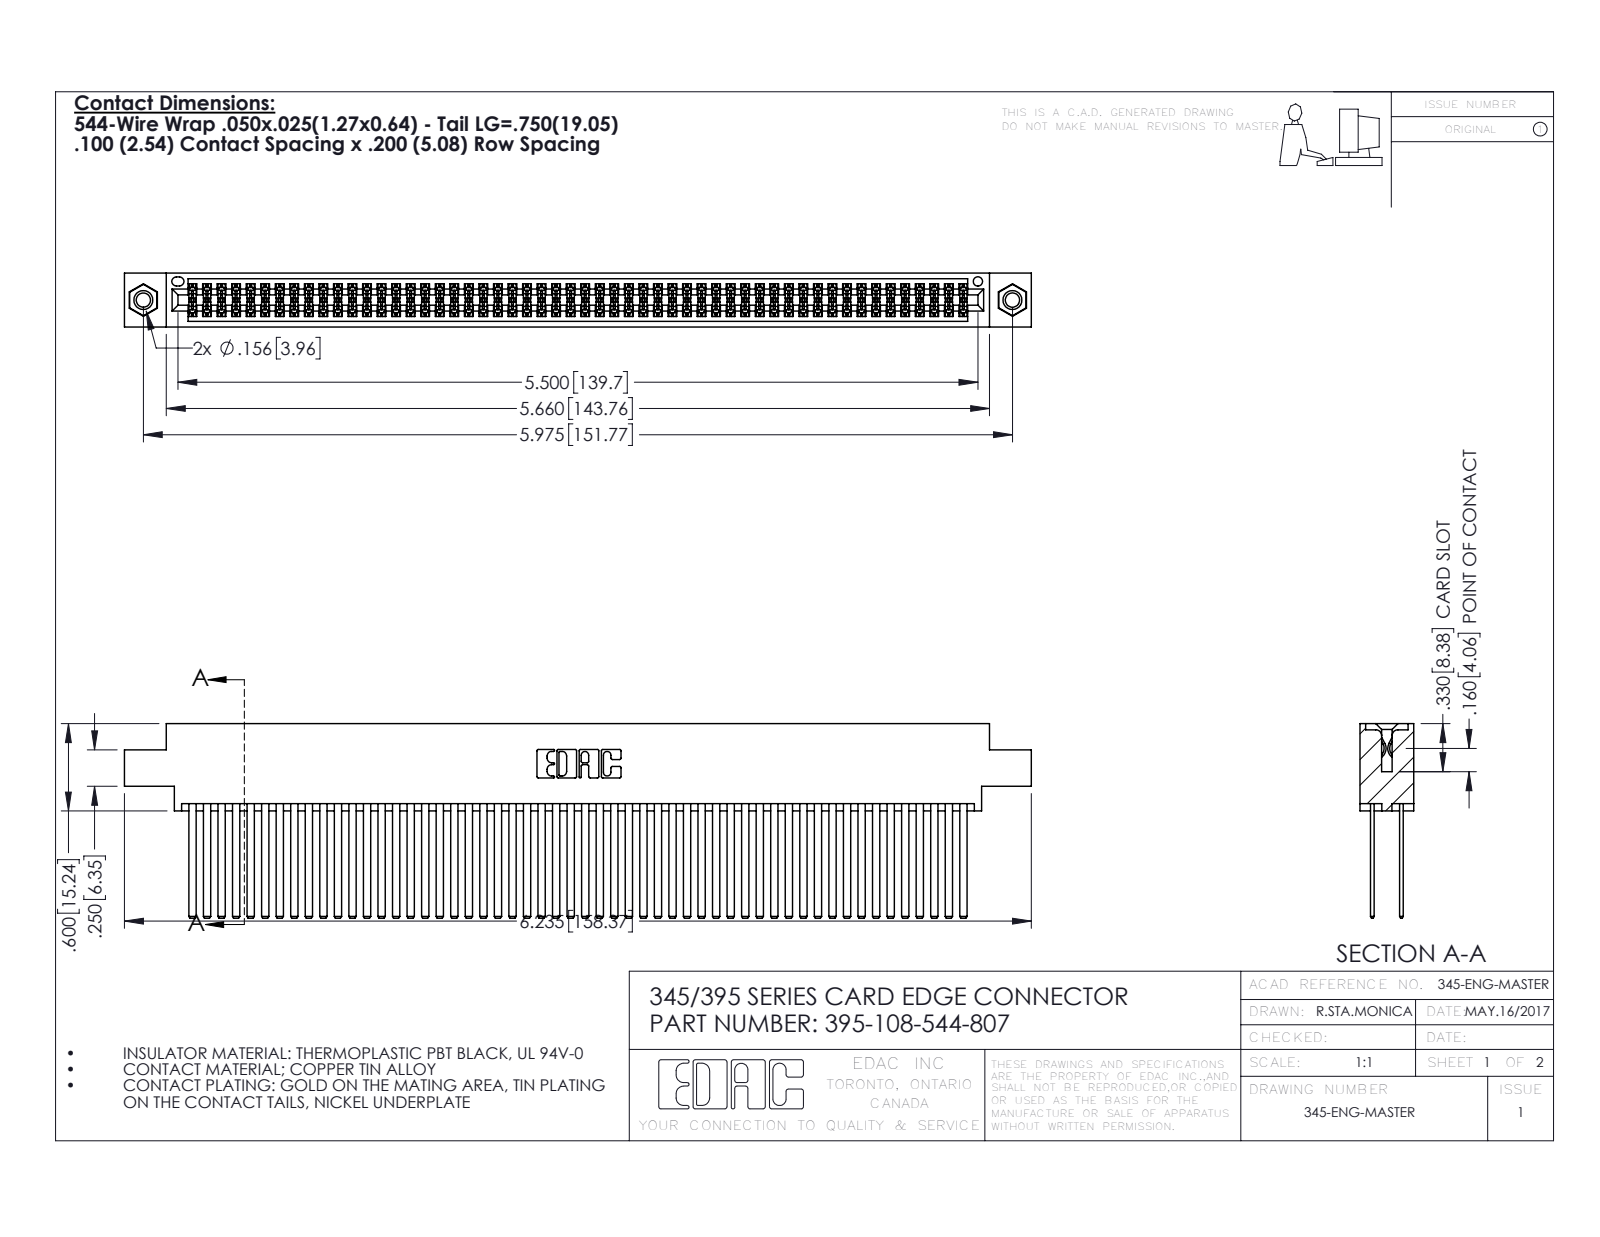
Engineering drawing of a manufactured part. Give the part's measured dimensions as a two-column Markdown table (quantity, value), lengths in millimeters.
| quantity | value |
| --- | --- |
| part name | 395-108-544-807; 345 Part_0.170 Offset - 0.156 Dia-TI; 345-250-001_345-250-005-103; 345-292-001_345-293-144 |
| STEP written by | SolidWorks 2016 (CONFIG_CONTROL_DESIGN) |
| units | millimeters |
| bodies | 111 solids, 4942 faces (3248 planar, 1678 cylindrical, 16 other) |
| overall size | 158.4 × 34 × 9.4 |
| volume | 16 880 mm³ |
| surface area | 29 790 mm² |
| round holes (diameter × count) | 2.5 × 2, 3.2 × 2, 4 × 2, 1.6 × 1 |
| round bosses / shafts (diameter × count) | 3.9 × 2 |
| partial cylindrical surfaces (radius × count) | 0.2 × 162, 0.3 × 22, 0.2 × 6, 0.8 × 6, 0.7 × 3, 0.4 × 2, 0.5 × 2, 0.6 × 2 |
| main face-to-face distances | 5.1, 0.6, 1.8, 2.5, 6.9, 7.6, 5.7, 4.4, 9.4, 3.8 |
| hole center spacings | 6.9, 145.8, 151.8 |
